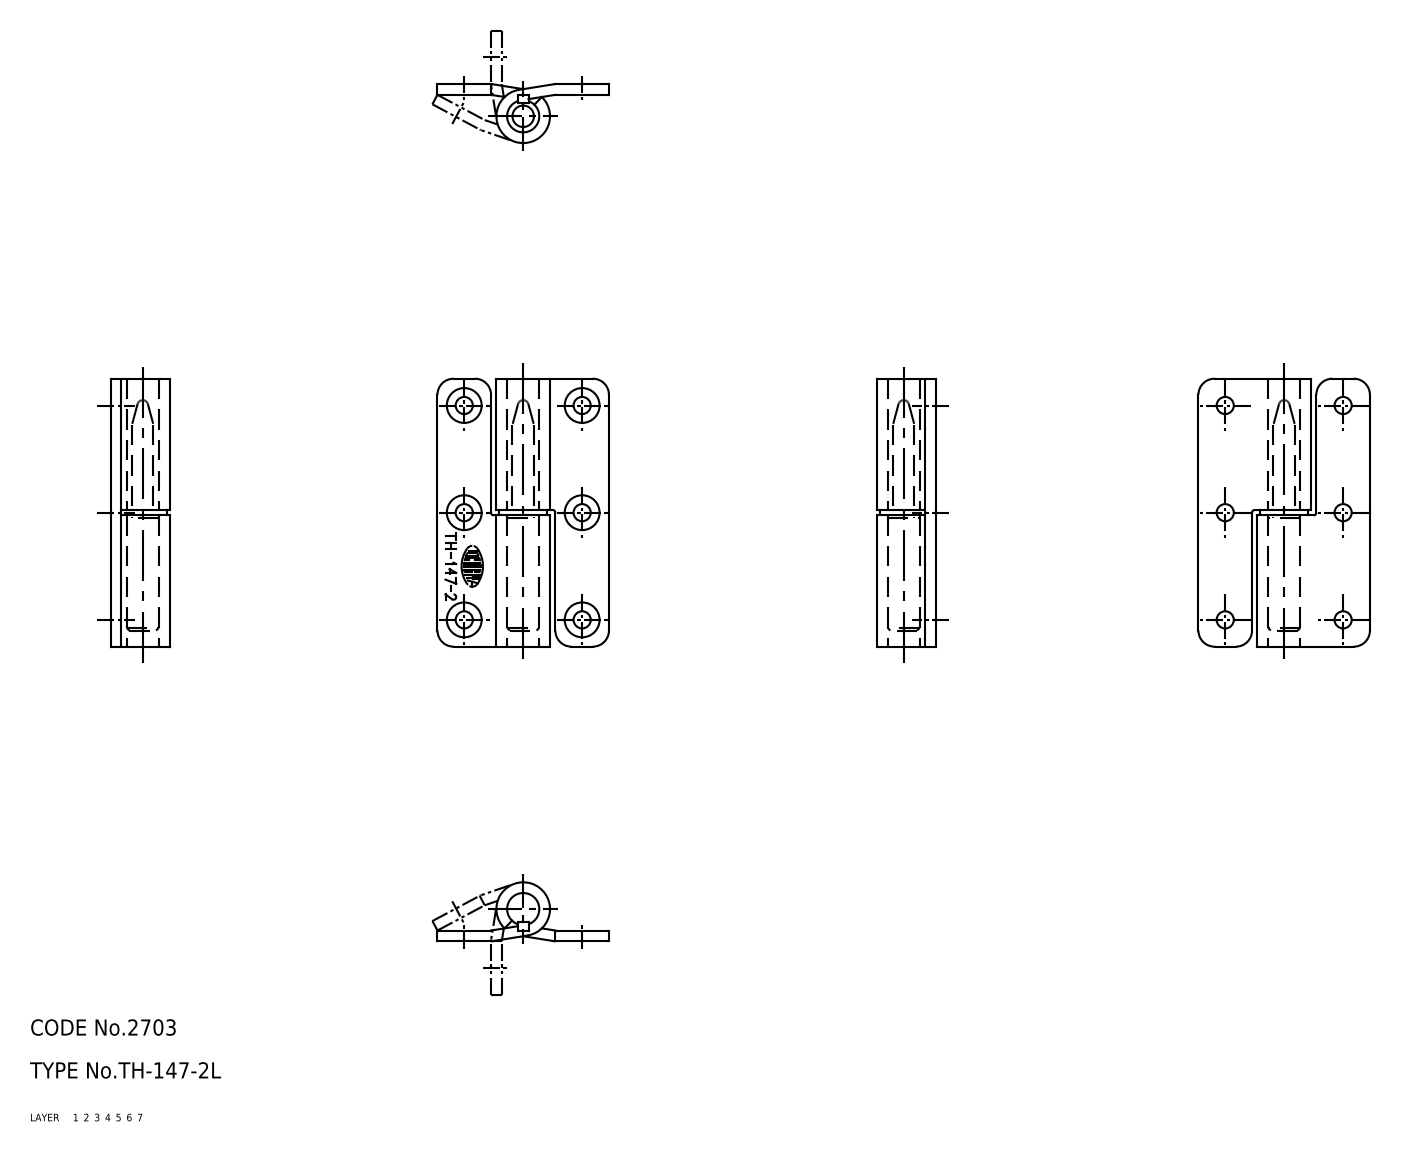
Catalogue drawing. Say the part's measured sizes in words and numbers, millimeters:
The part is named "67113659; 67113672; 67113685; 67113698". Its 3-D file was written by "CADfix (AUTOMOTIVE_DESIGN)". It is 4 solids with 83 faces: 0 planar, 0 cylindrical and 83 other. Overall it measures 50 by 32 by 11 millimeters. Its volume is 5 408 cubic millimeters and its surface area 6 240 square millimeters.
